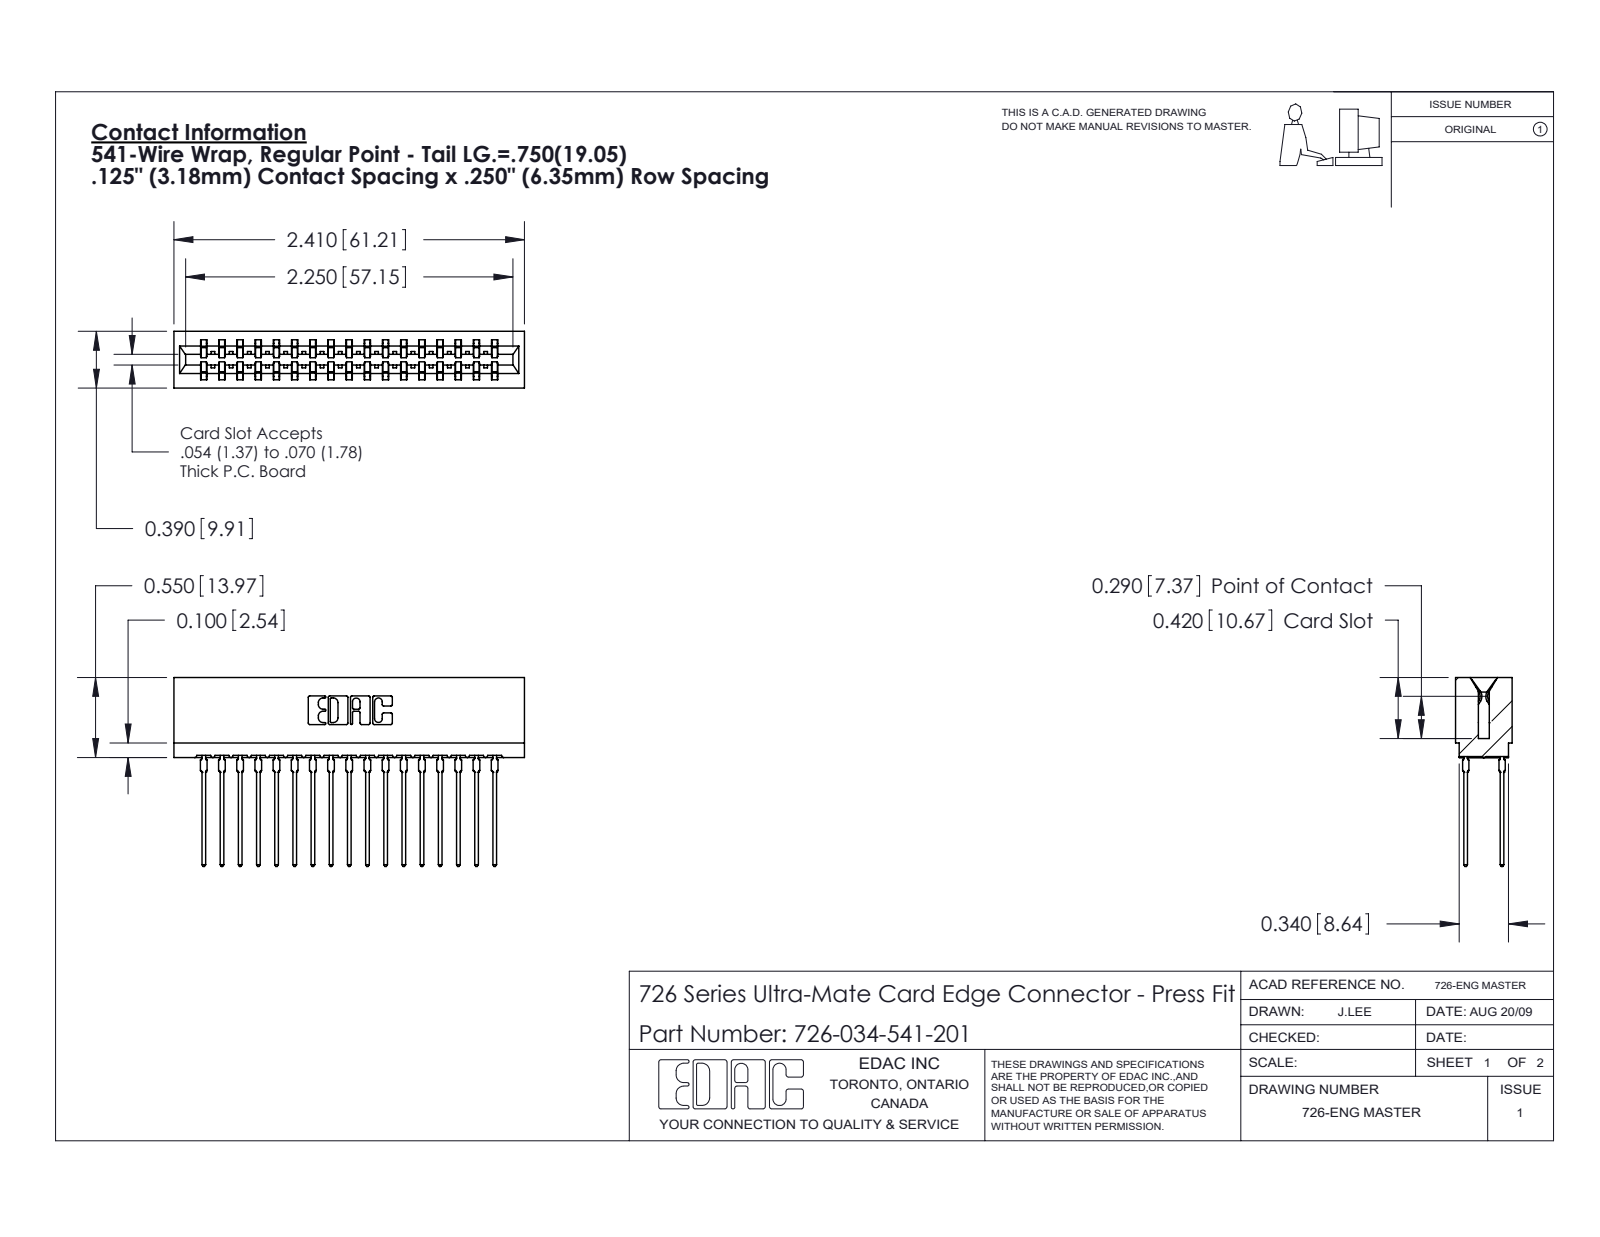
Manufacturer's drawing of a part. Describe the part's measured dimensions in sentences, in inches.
The part is named "726 Part_.515 Slot Depth - 01; 746-292-001_541; 726-034-541-201". Its 3-D file was written by "SolidWorks 2020 (CONFIG_CONTROL_DESIGN)". It is 35 solids with 3140 faces: 1619 planar, 637 cylindrical and 884 other. Overall it measures 2.41 by 1.299 by 0.39 inches. Its volume is 0.363 cubic inches and its surface area 16.03 square inches. Partial cylindrical surfaces (rounded edges, fillets, slot ends): 68 of radius 0.021, 22 of radius 0.01, 18 of radius 0.015, 8 of radius 0.005, 8 of radius 0.011, 6 of radius 0.007, 6 of radius 0.031, 3 of radius 0.026. The main face-to-face distances are 0.057, 0.333, 0.25, 0.025, 0.307, 0.083, 0.39, 0.275, 0.5, 0.75.
